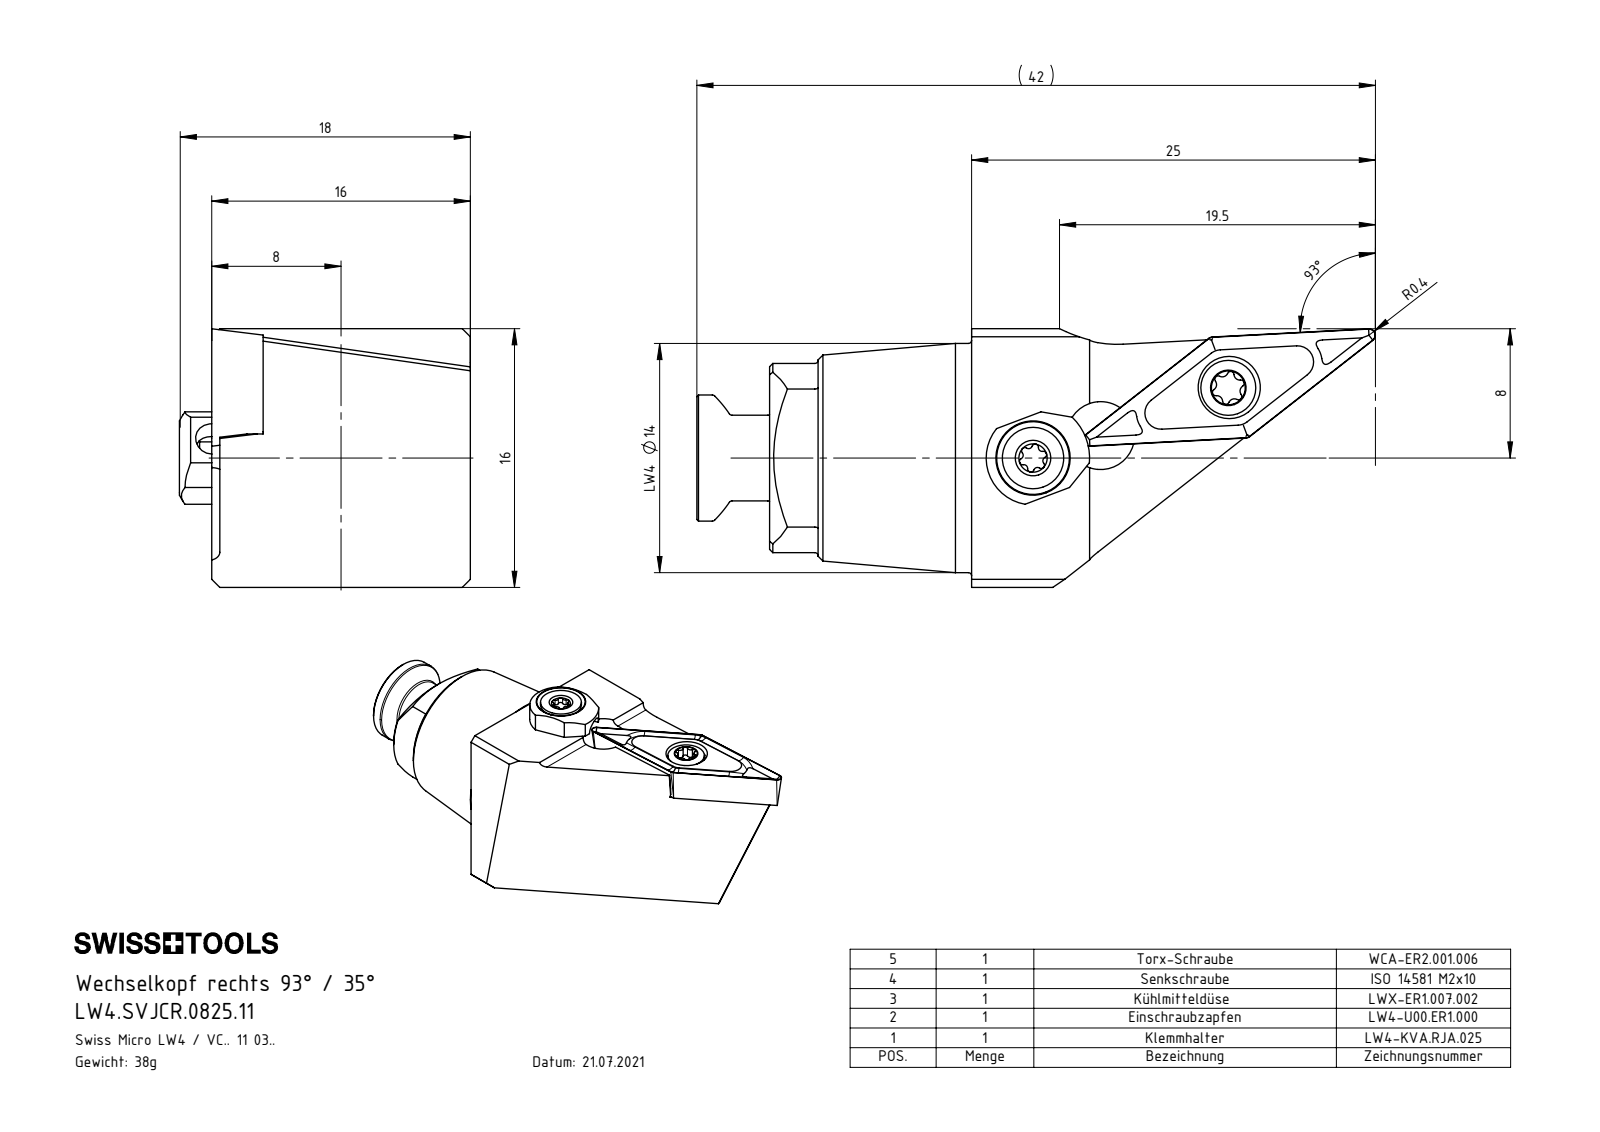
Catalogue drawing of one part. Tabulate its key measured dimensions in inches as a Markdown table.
| quantity | value |
| --- | --- |
| part name | LW4-U00.ER1.000_B; ISO 14581 - M2x10; LWX-ER1.007.002; VCGT110304 (+3 more) |
| STEP written by | SolidWorks 2022 (CONFIG_CONTROL_DESIGN) |
| units | inches |
| bodies | 6 solids, 262 faces (70 planar, 83 cylindrical, 109 other) |
| overall size | 1.653 × 0.709 × 0.63 |
| volume | 0.286 in³ |
| surface area | 4.962 in² |
| round holes (diameter × count) | 0.079 × 2, 0.063 × 1, 0.081 × 1, 0.098 × 1, 0.11 × 1, 0.118 × 1, 0.152 × 1, 0.165 × 1, 0.217 × 1 |
| round bosses / shafts (diameter × count) | 0.558 × 1, 0.303 × 1, 0.236 × 1, 0.209 × 1, 0.197 × 1, 0.15 × 1, 0.134 × 1, 0.098 × 1 |
| partial cylindrical surfaces (radius × count) | 0.008 × 8, 0.008 × 6, 0.009 × 6, 0.014 × 4, 0.014 × 2, 0.02 × 1, 0.039 × 1, 0.114 × 1 |
| main face-to-face distances | 0.63, 0.505, 0.125, 0.295, 0.61, 0.106, 0.02, 0.079, 0.492, 0.157 |
| hole center spacings | 0.174, 0.33, 0.334, 0.504, 0.508 |
